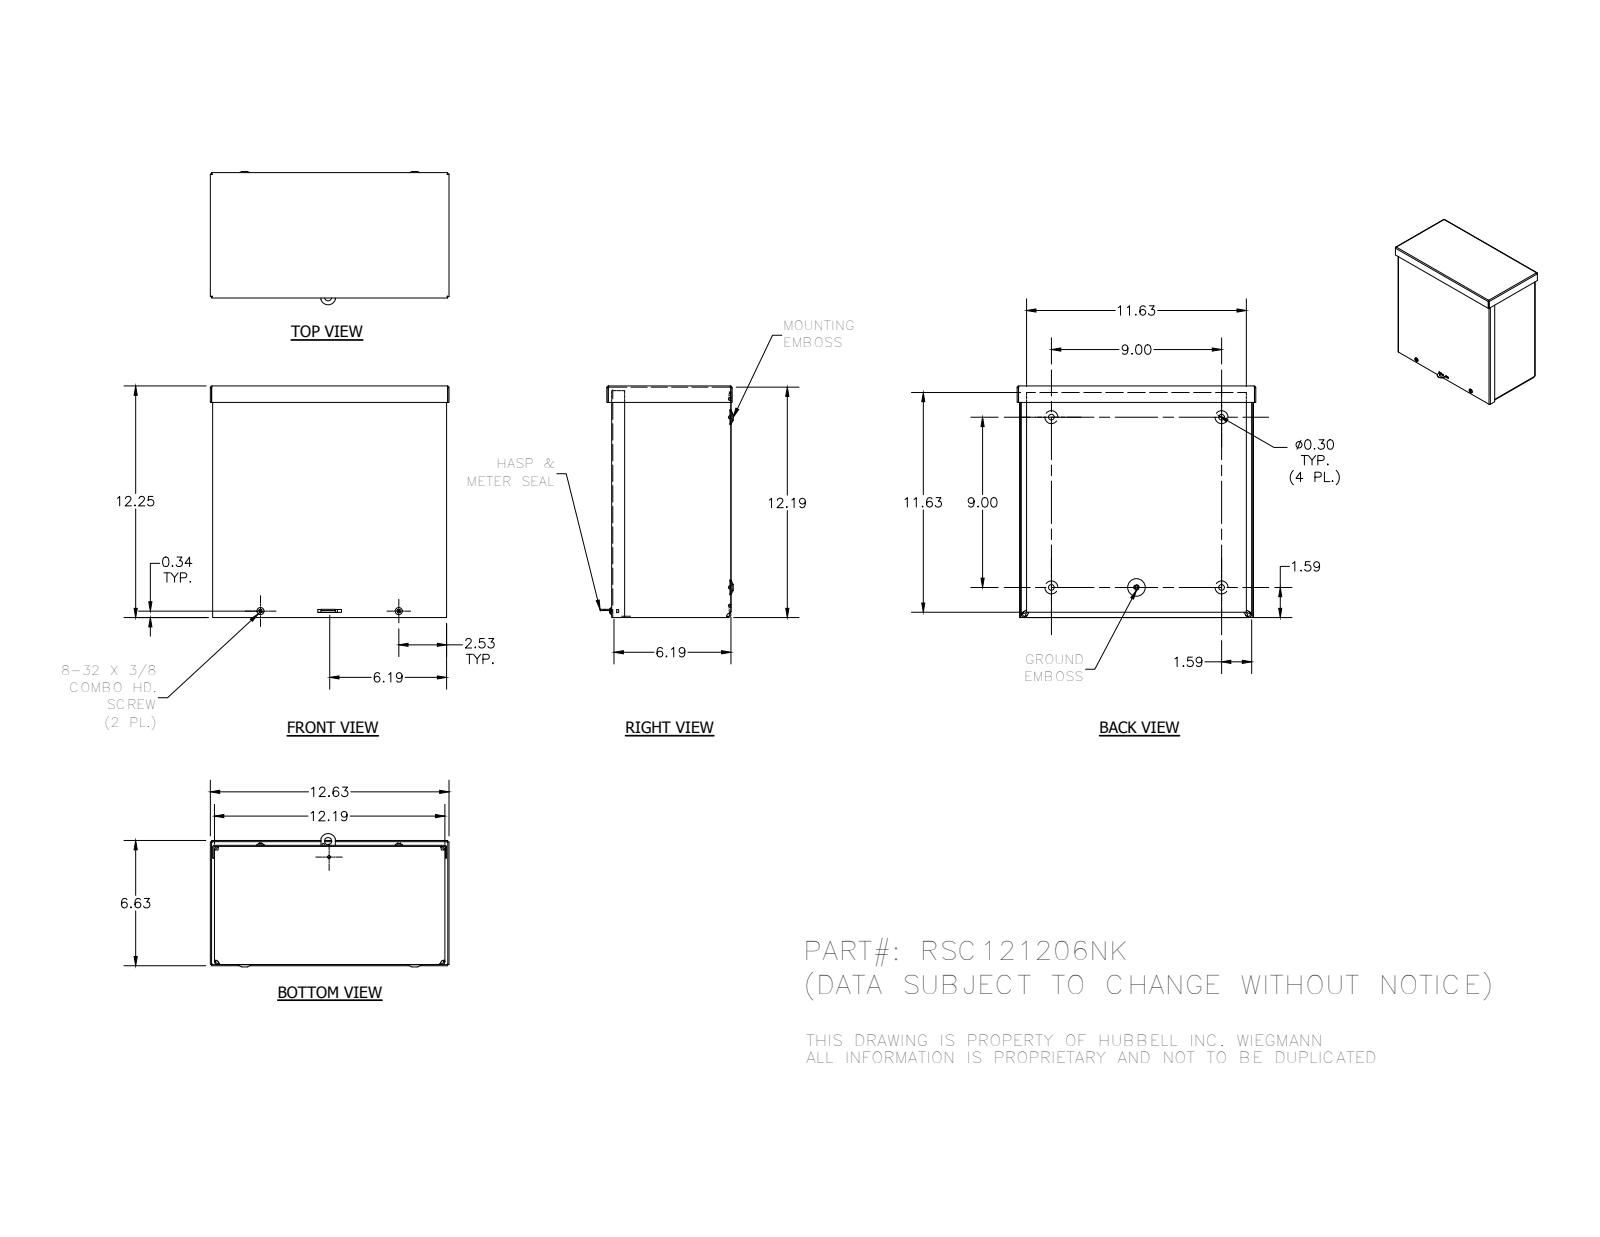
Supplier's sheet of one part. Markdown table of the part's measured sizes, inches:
| quantity | value |
| --- | --- |
| part name | RSC121206NK_WRAP; RSC1212NK_LID; RSC1206NK_CAP; 3183 (+3 more) |
| STEP written by | Autodesk Inventor 2014 (AUTOMOTIVE_DESIGN) |
| units | inches |
| bodies | 7 solids, 377 faces (163 planar, 78 cylindrical, 136 other) |
| overall size | 12.625 × 12.25 × 7.125 |
| volume | 48.35 in³ |
| surface area | 1 576 in² |
| round holes (diameter × count) | 0.3 × 4, 0.313 × 4, 0.148 × 2, 0.125 × 1, 0.136 × 1, 0.156 × 1, 0.165 × 1, 0.375 × 1 |
| round bosses / shafts (diameter × count) | 0.384 × 2, 0.164 × 2, 0.228 × 1 |
| partial cylindrical surfaces (radius × count) | 0.031 × 8, 0.093 × 8, 0.125 × 8, 0.187 × 8, 0.055 × 4, 0.062 × 4, 0.094 × 4, 0.117 × 4 |
| main face-to-face distances | 0.062, 12.126, 0.062, 6.249, 6.187, 12.188, 0.063, 6.312, 6.25, 0.124 |
| hole center spacings | 9, 1.356, 4.5, 7.313, 10.062, 10.096, 10.286, 11.312 |
